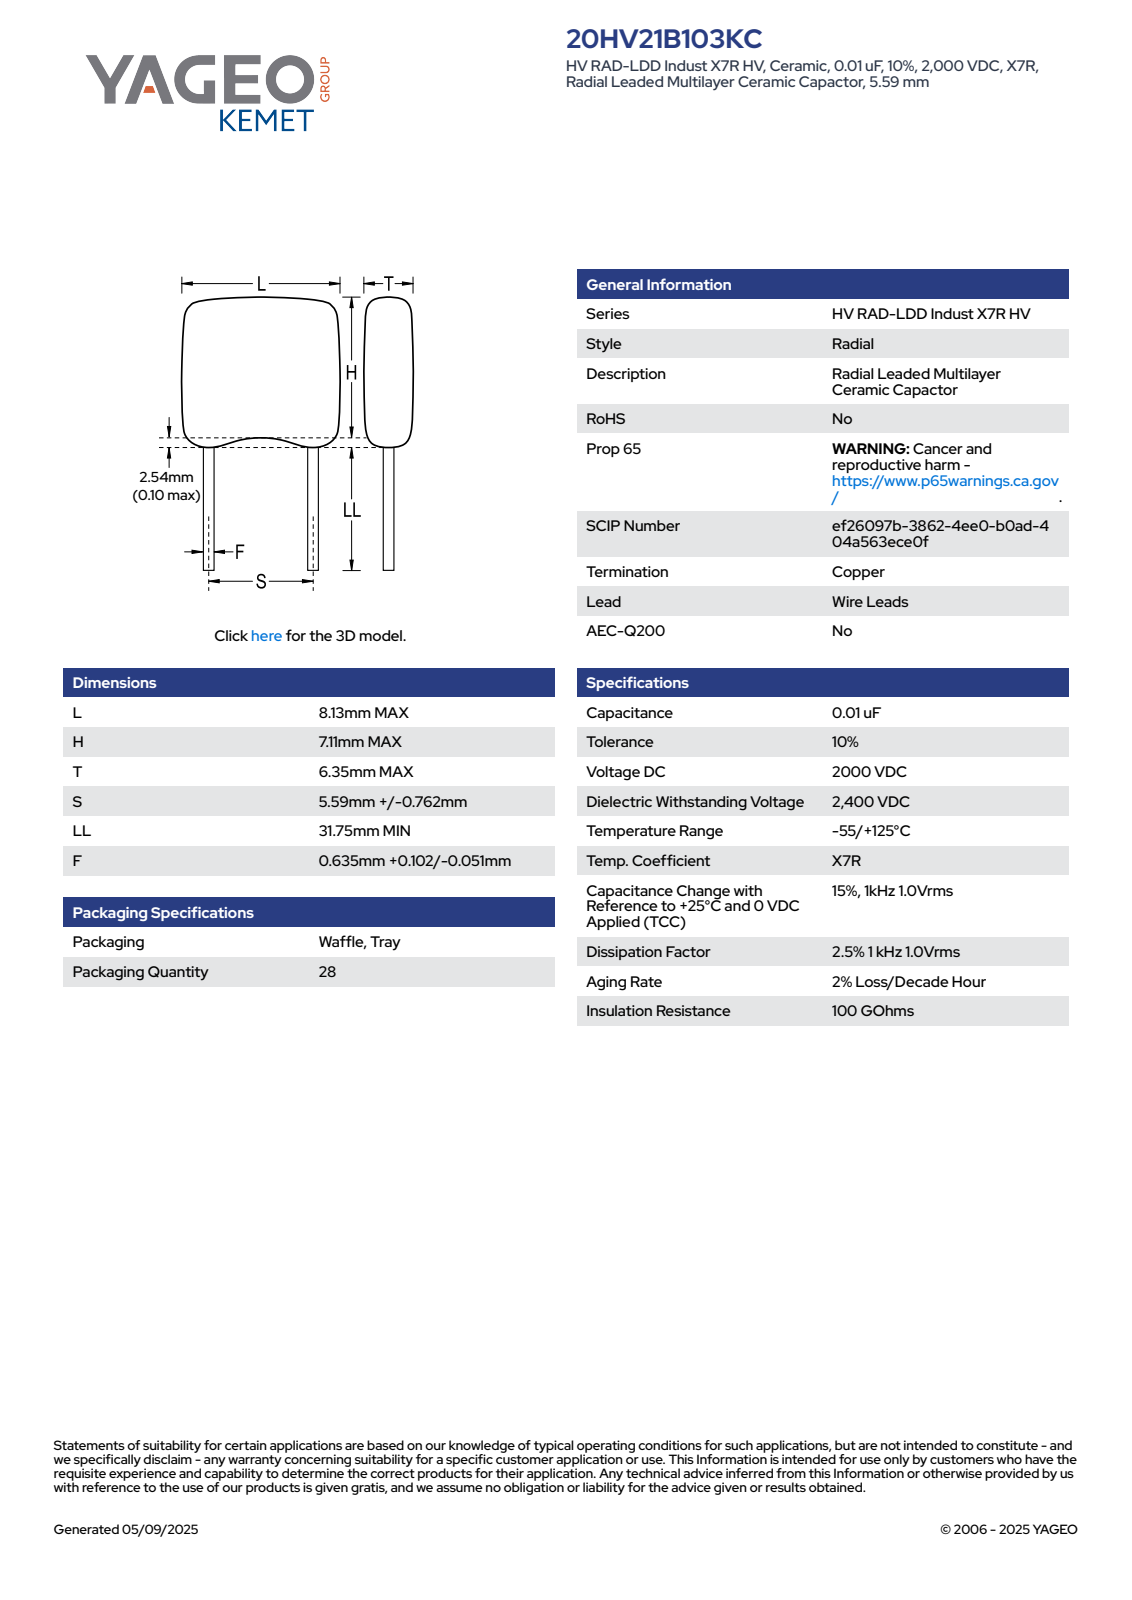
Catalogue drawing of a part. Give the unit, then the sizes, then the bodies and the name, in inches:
Units: inches
Overall size (bounding box): 0.467 × 0.32 × 0.25
Round bosses / shafts (diameter × count): ⌀0.029 ×2
Partial cylindrical surfaces — rounded edges, fillets, slot ends (radius × count): R0.039 ×8, R0.02 ×4
Main face-to-face distances: 0.25, 0.32, 0.342, 0.125, 0.467, 0.317, 0.192, 0.15, 0.276, 0.152
Volume: 0.024 in³ · Surface area: 0.525 in²
Bodies: 4 solids, 94 faces (66 planar, 18 cylindrical, 10 other)
Part name (STEP PRODUCT): CCRM_RCST_HV21_L8.13H7.11T6.35S5.59LL31.75F0.737
STEP written by: SolidWorks 2021 (AUTOMOTIVE_DESIGN)
